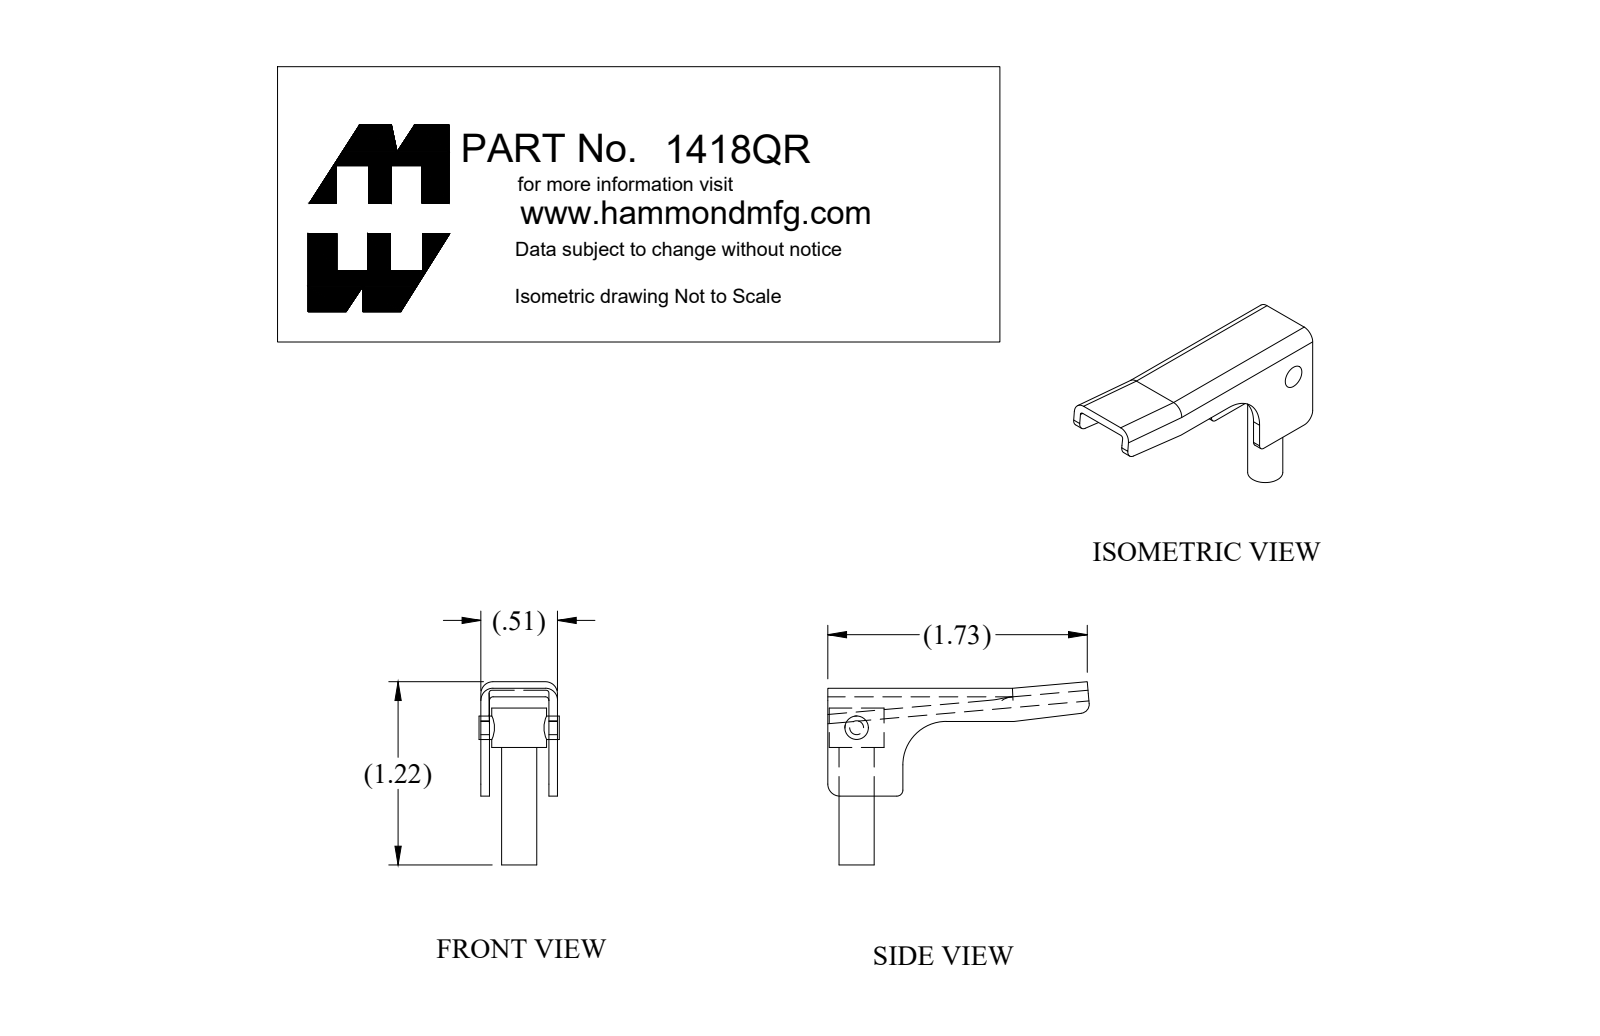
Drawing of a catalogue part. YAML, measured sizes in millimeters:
part_name: "1418QR_Default"
step_written_by: "SolidWorks 2019 (CONFIG_CONTROL_DESIGN)"
units: millimeters
bodies: {solids: 2, faces: 53, planar: 25, cylindrical: 28, other: 0}
overall_size: [44.2, 31, 13.6]
volume: 2820
surface_area: 3456
round_holes:
  - {diameter: 2.3, count: 1}
round_bosses_or_shafts:
  - {diameter: 9.3, count: 1}
  - {diameter: 5.9, count: 1}
  - {diameter: 4, count: 1}
partial_cylinders:
  - {radius: 2, count: 5}
  - {radius: 0.5, count: 2}
  - {radius: 0.6, count: 2}
  - {radius: 1, count: 1}
  - {radius: 1.5, count: 1}
  - {radius: 7.3, count: 1}
face_to_face_distances: [1.4, 11.5, 13, 10.1, 1.9, 3.4, 6.7, 8.6, 10, 4.4]
